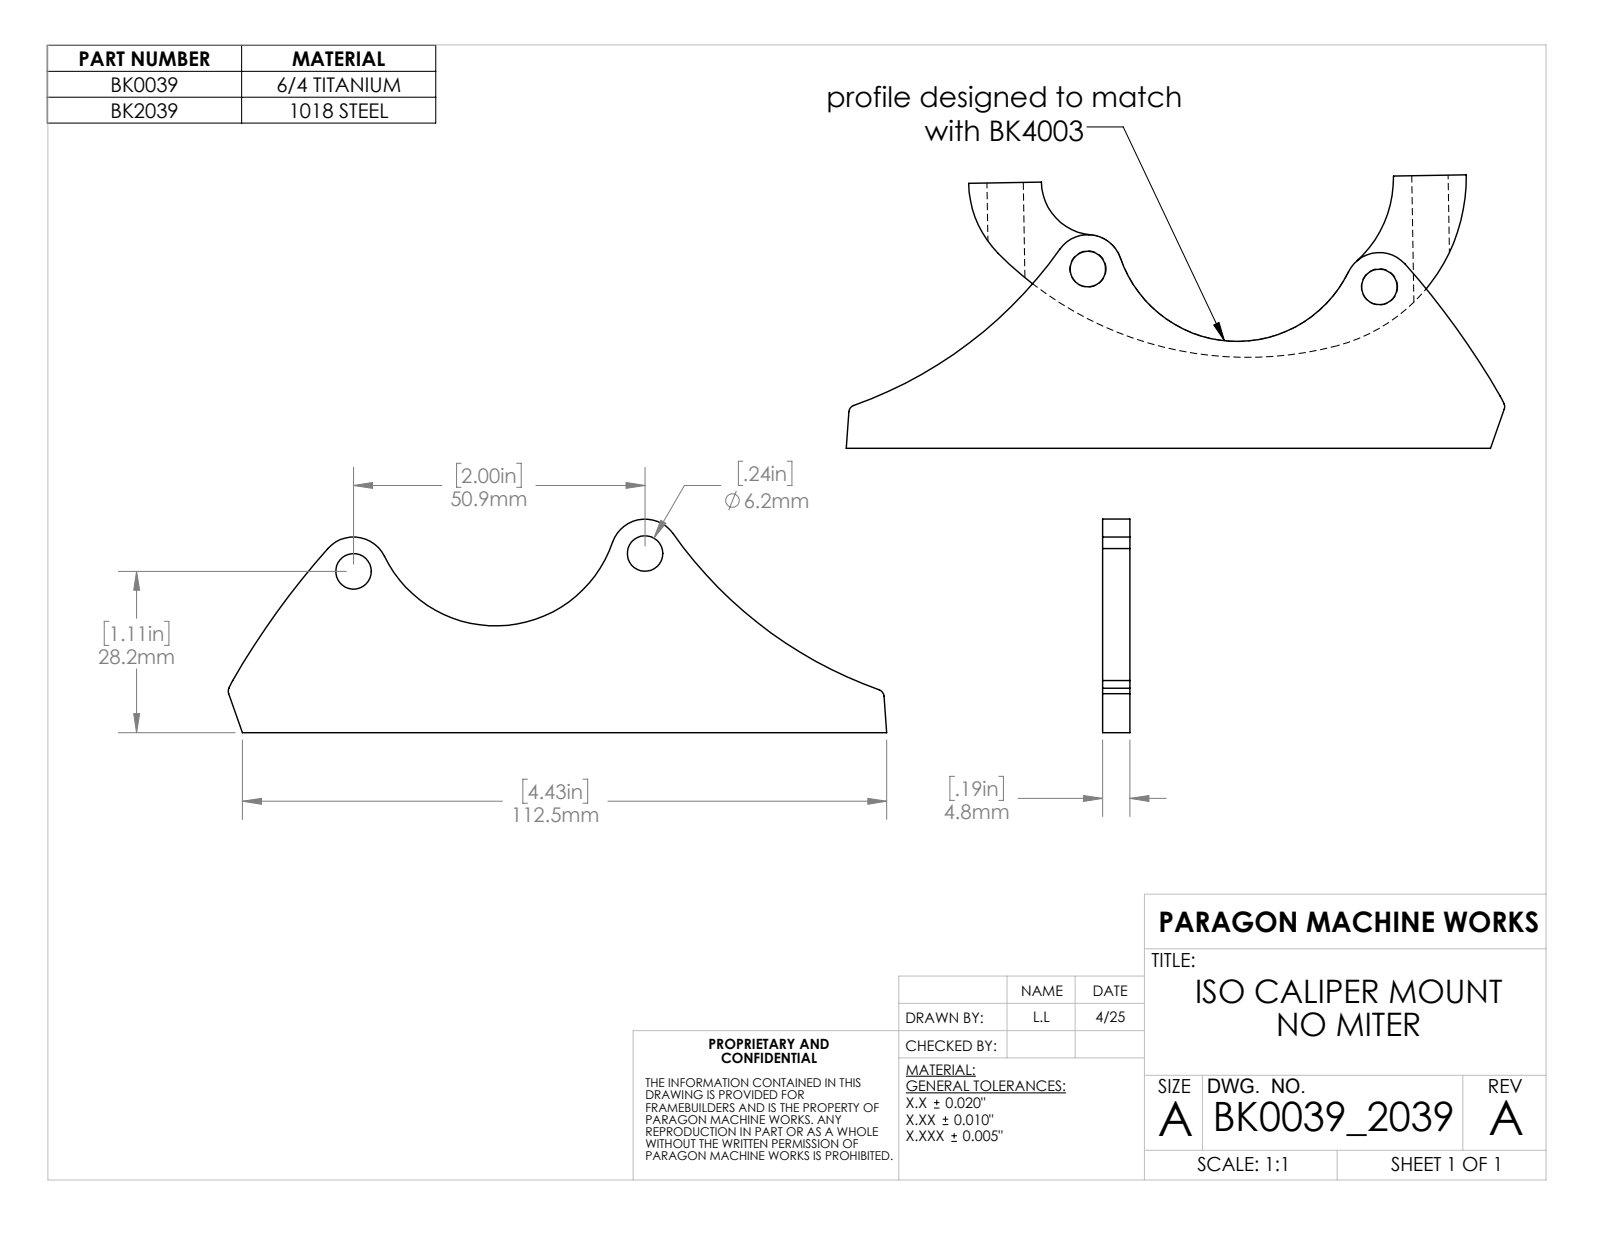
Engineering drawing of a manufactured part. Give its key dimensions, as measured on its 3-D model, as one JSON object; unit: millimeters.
{"step_written_by": "Mastercam 2018 ... CNC Software, Inc. (AUTOMOTIVE_DESIGN)", "units": "millimeters", "bodies": {"solids": 1, "faces": 15, "planar": 5, "cylindrical": 10, "other": 0}, "overall_size": [373.4, 191.6, 4.8], "volume_mm3": 12200, "surface_area_mm2": 6639, "round_holes": [[6.2, 2]], "partial_cylinders_radius": [[6, 2], [1.3, 1], [1.3, 1], [13.9, 1], [21.6, 1], [74.6, 1], [137.6, 1]], "face_to_face_distances": [4.7], "hole_center_spacings": [51]}
